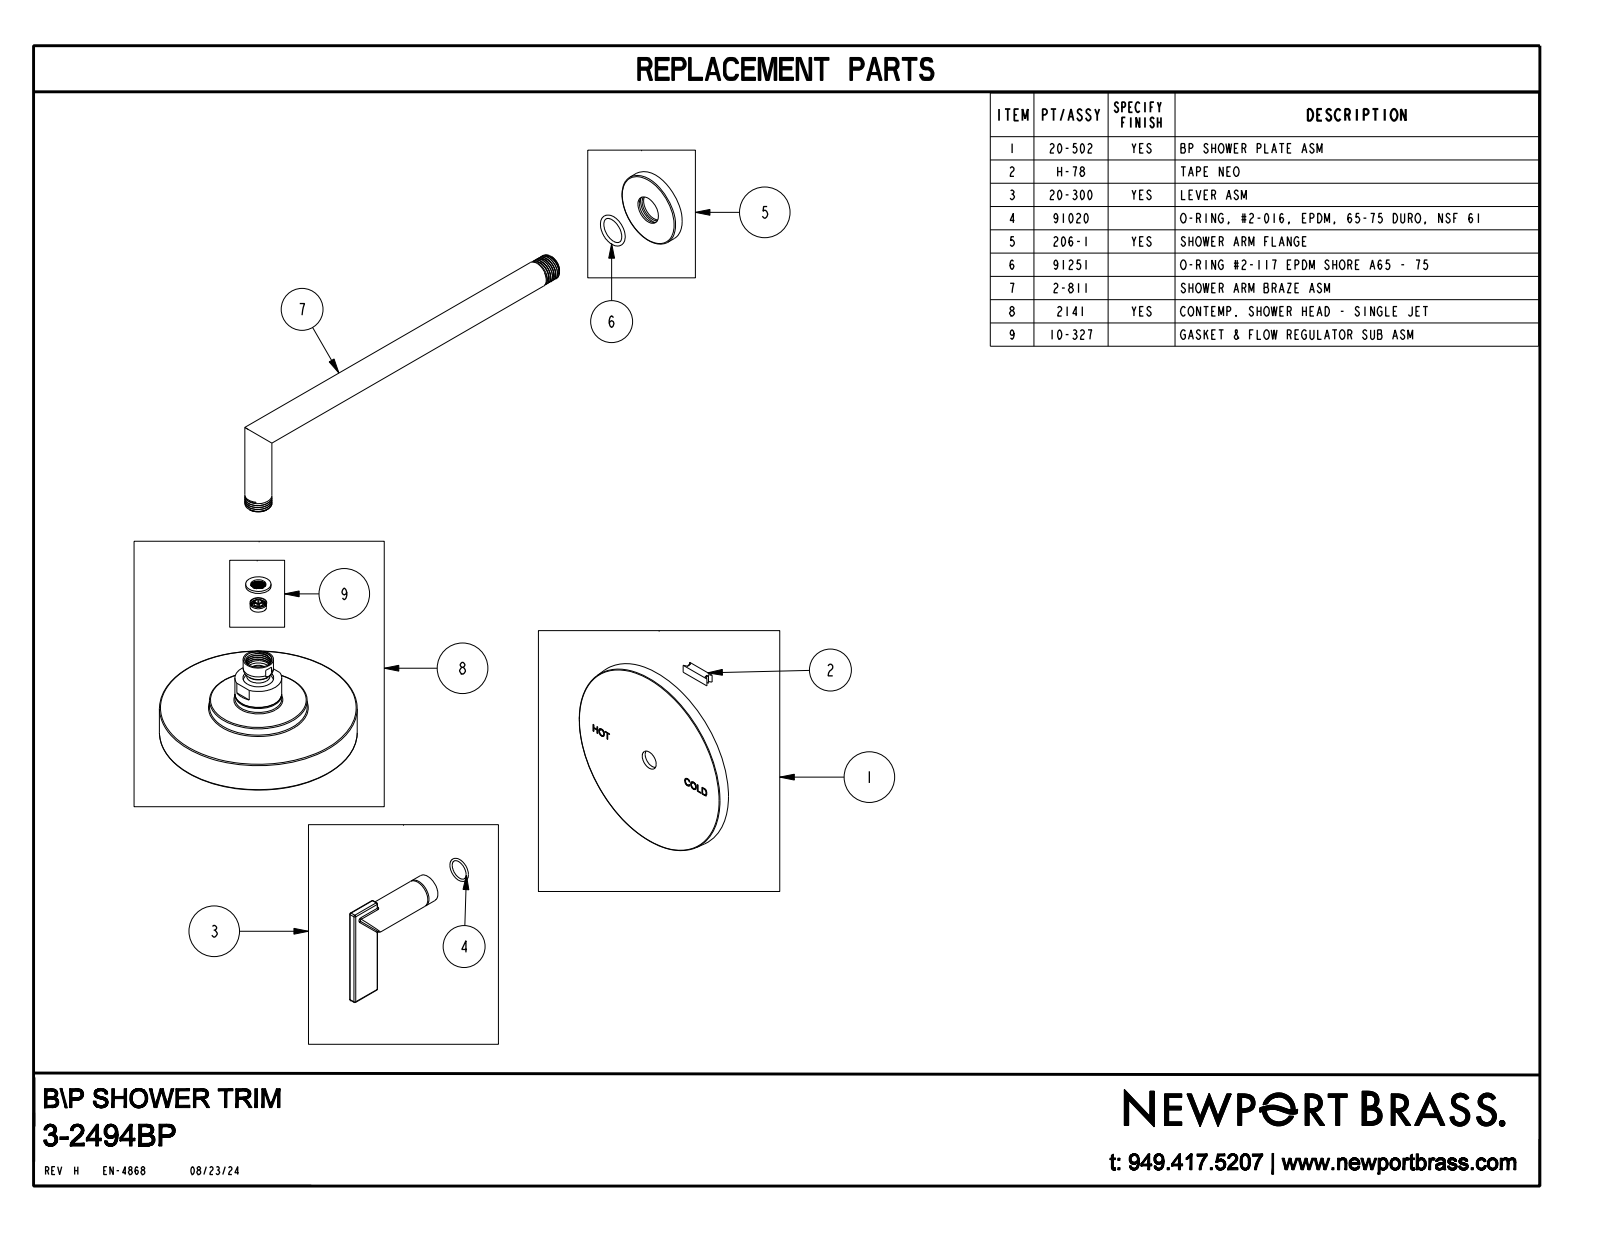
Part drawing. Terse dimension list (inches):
name: 3-2494BP
written by: CREO PARAMETRIC BY PTC INC, 2018400 (CONFIG_CONTROL_DESIGN)
unit: in
bodies: 2 solids, 1026 faces (164 planar, 226 cylindrical, 636 other)
size: 19.125 × 14.605 × 6
volume: 54.61 in³; area: 208.5 in²
holes: 90× ⌀0.05, 1× ⌀0.22, 1× ⌀5.256
bosses: 2× ⌀0.813, 1× ⌀5.91, 1× ⌀5.22, 1× ⌀2.92, 1× ⌀2.25, 1× ⌀1.4, 1× ⌀0.905, 1× ⌀0.86
rounds: 16× R0.04
face distances: 0.35, 0.291, 0.31, 0.04, 0.236, 1.084, 0.793, 3.55, 3.24, 3.2
hole spacings: 0.851, 0.98, 0.98, 1.698, 1.41, 0.55, 0.507, 0.574
